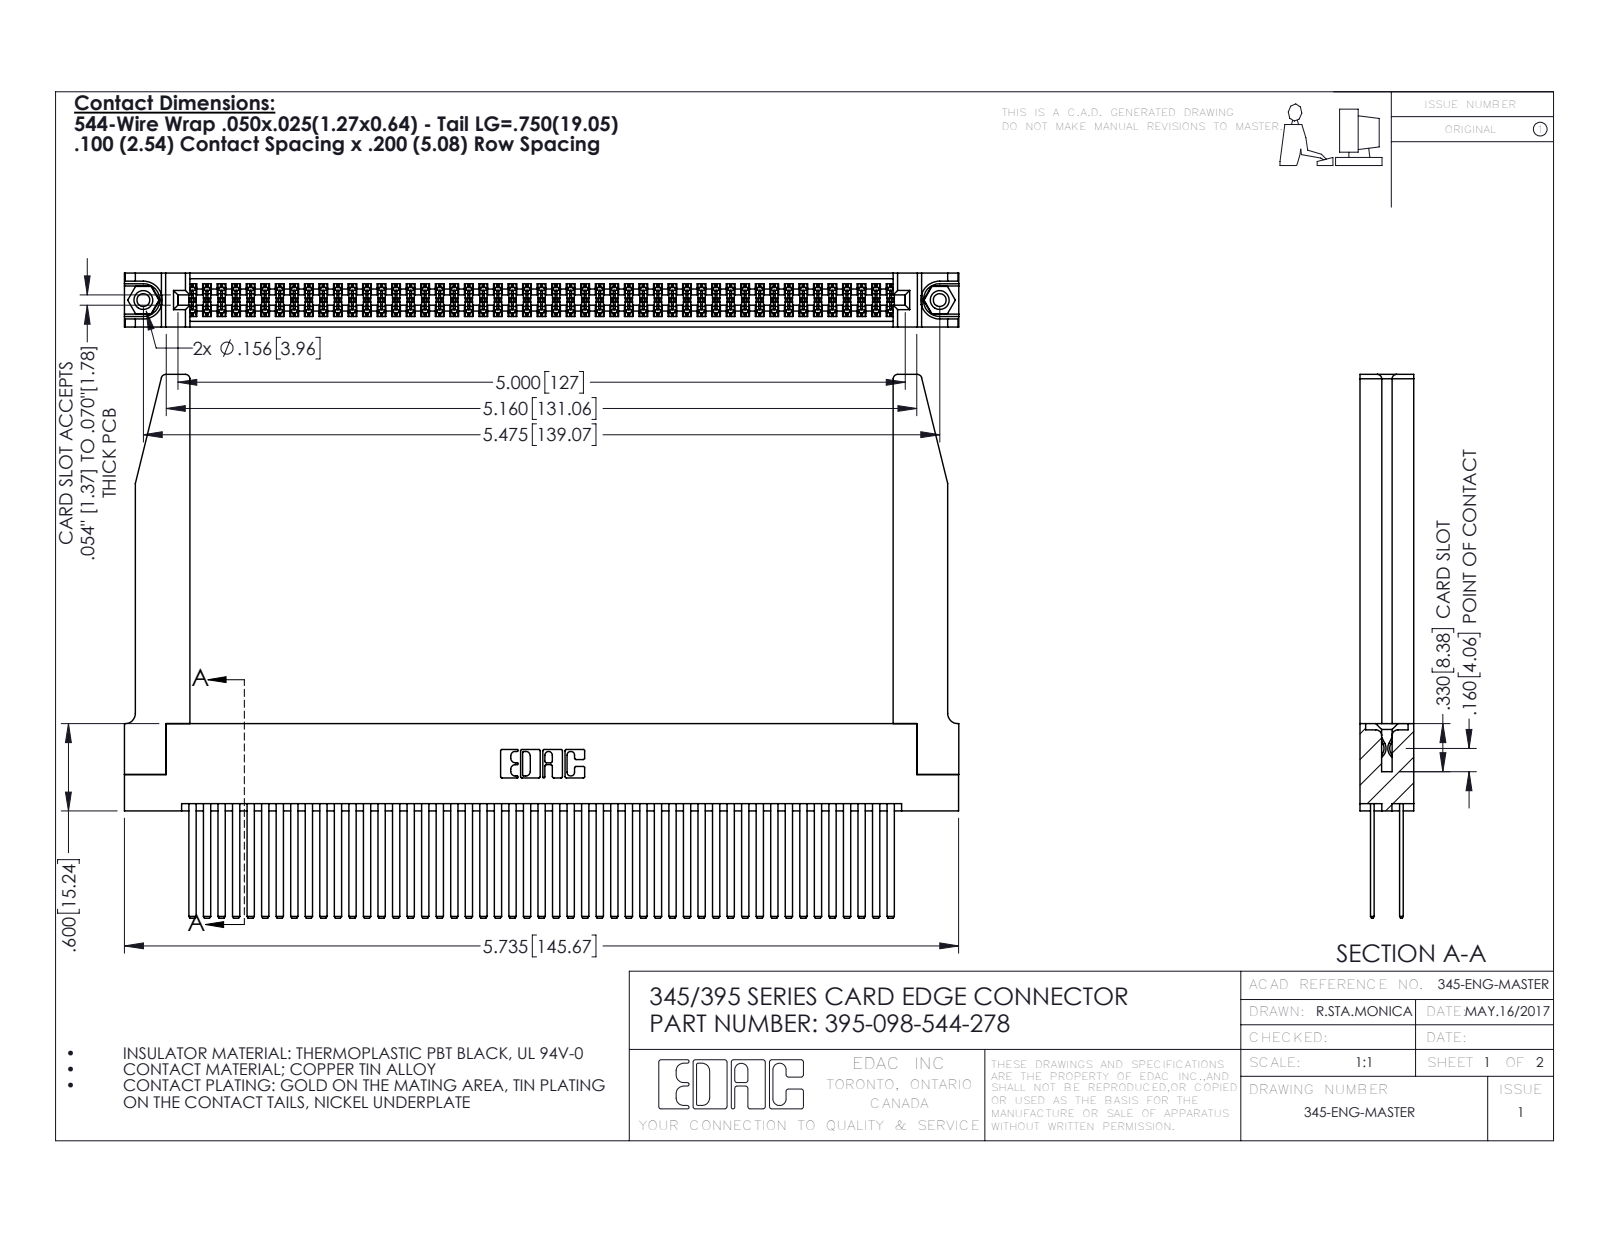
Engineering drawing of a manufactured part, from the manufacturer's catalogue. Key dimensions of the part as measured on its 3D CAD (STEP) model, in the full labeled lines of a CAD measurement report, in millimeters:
Part name (STEP PRODUCT): 345 Part_Flush Mounting Lugs - 0.156 Dia-TH; 395-098-544-278; 345-292-001_345-293-144; 345-250-001_345-250-001-102 (+1 more)
STEP written by: SolidWorks 2016 (CONFIG_CONTROL_DESIGN)
Units: millimetres
Bodies: 103 solids, 4672 faces (3064 planar, 1556 cylindrical, 52 other)
Overall size (bounding box): 145.7 × 94.9 × 9.4
Volume: 23 370 mm³ · Surface area: 34 050 mm²
Round holes (diameter × count): ⌀2.3 ×2, ⌀3.2 ×2, ⌀4 ×2, ⌀1.6 ×1
Round bosses / shafts (diameter × count): ⌀3.9 ×2
Partial cylindrical surfaces — rounded edges, fillets, slot ends (radius × count): R0.2 ×147, R0.3 ×22, R0.8 ×8, R0.2 ×6, R0.8 ×6, R0.7 ×3, R0.4 ×2, R0.5 ×2
Main face-to-face distances: 1.8, 7.6, 5.1, 2.5, 6.9, 0.6, 9.4, 5.7, 4.4, 3.8
Hole centre spacings: 6.9, 133.1, 139.1
